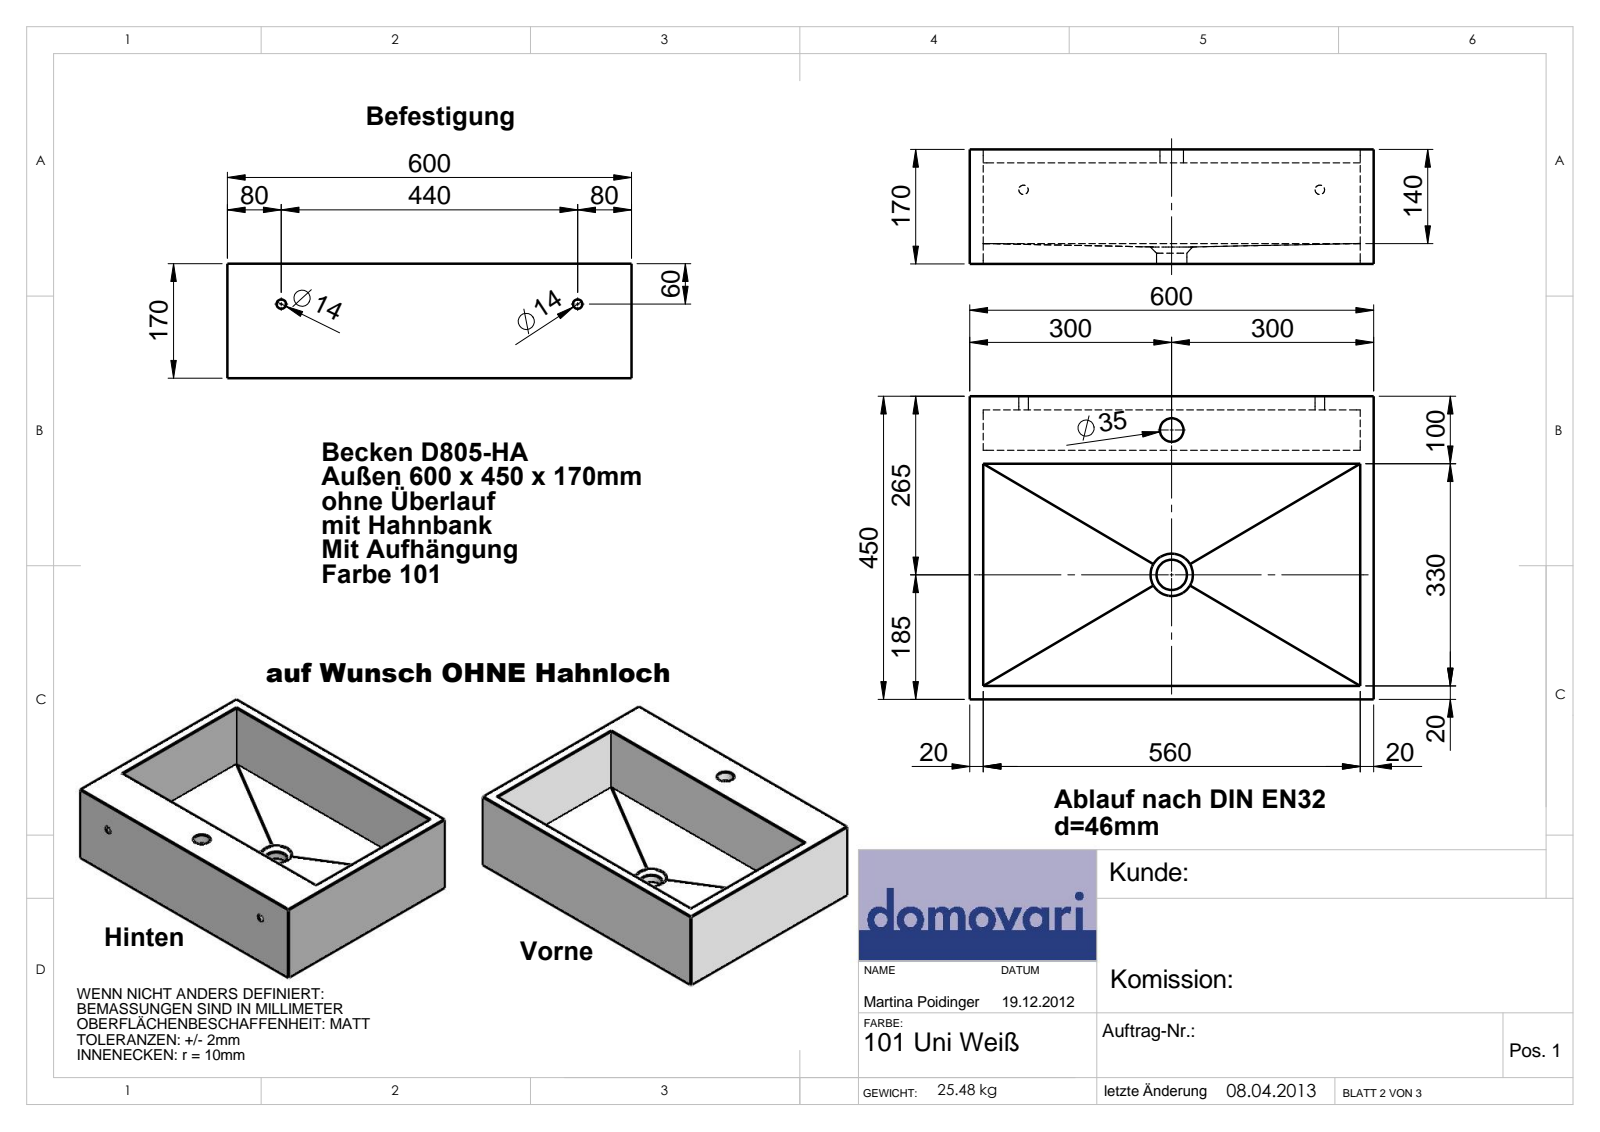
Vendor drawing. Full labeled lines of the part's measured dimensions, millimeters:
Part name (STEP PRODUCT): D805-HA
STEP written by: SolidWorks 2017 (AUTOMOTIVE_DESIGN)
Units: millimetres
Bodies: 0 solids, 31 faces (15 planar, 6 cylindrical, 10 other)
Overall size (bounding box): 600 × 450 × 170
Round holes (diameter × count): ⌀14 ×2, ⌀45 ×1
Main face-to-face distances: 20, 80, 430, 350, 580, 450, 170, 370, 60, 410
Hole centre spacings: 440
